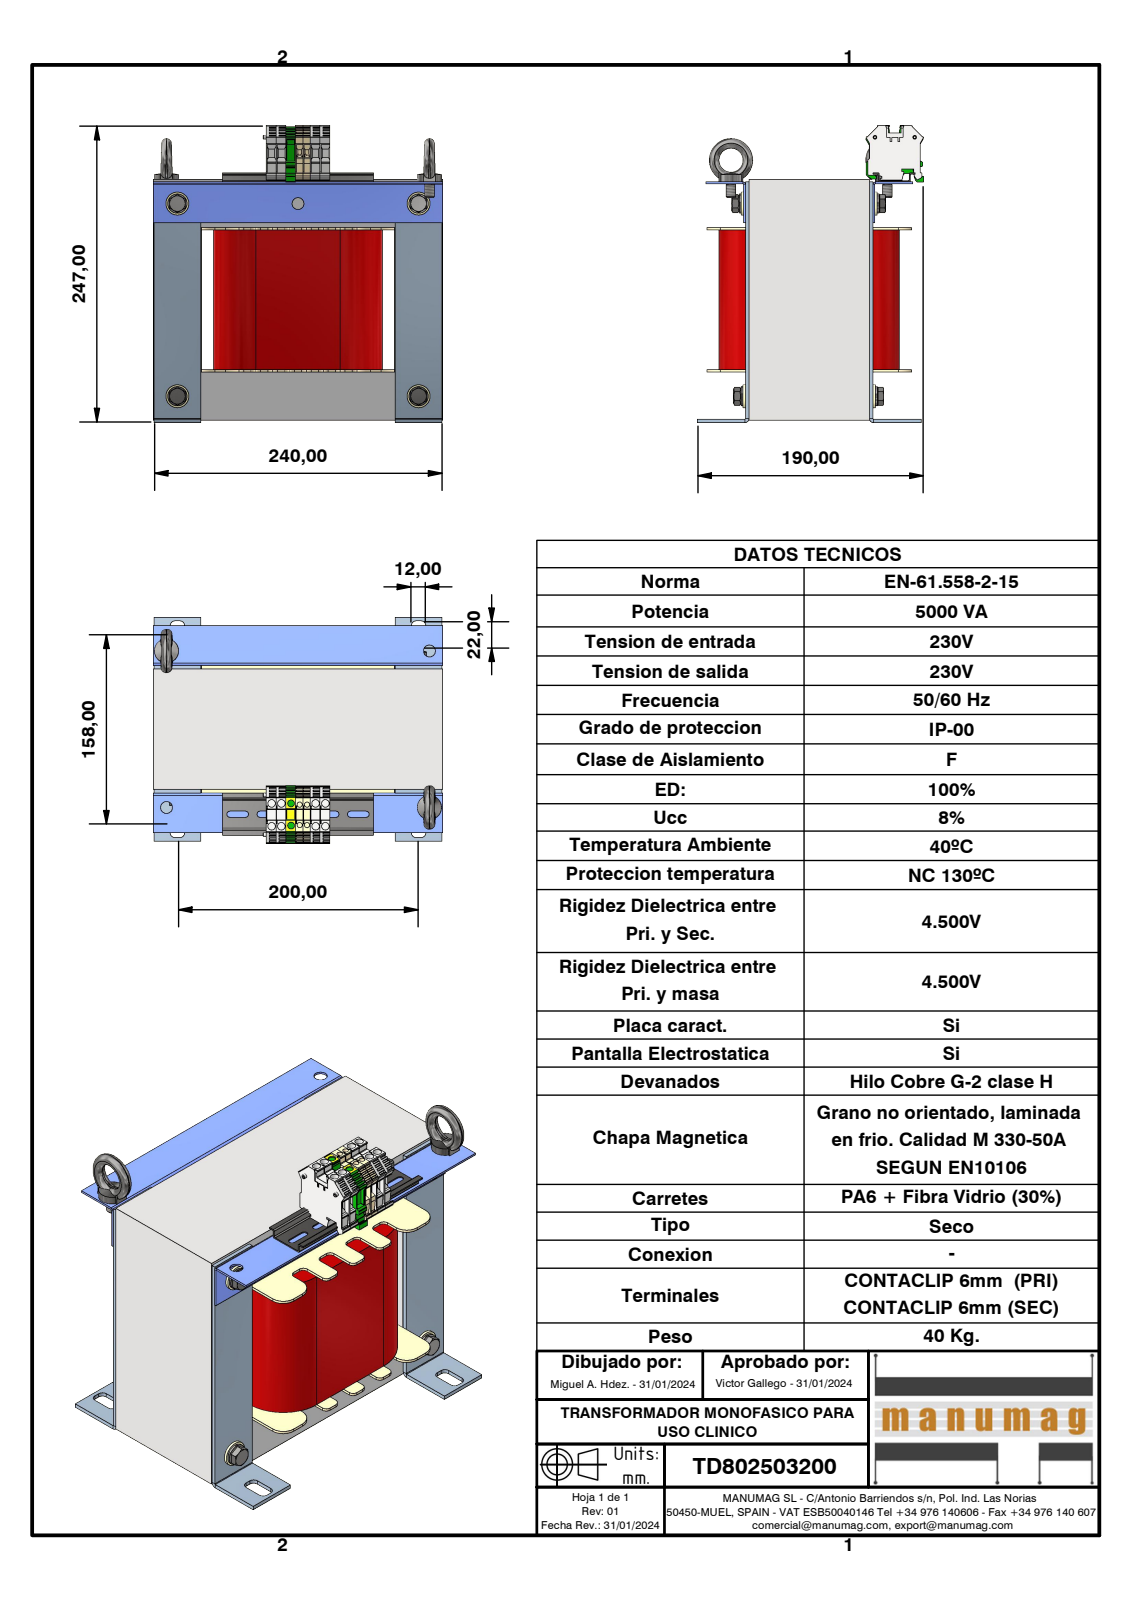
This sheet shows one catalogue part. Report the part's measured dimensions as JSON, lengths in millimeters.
{"part_name": "TD802503200; EI240 240 x 200 - 100 (Rc80); SEMI 40 X 60 RC80 EI240 - 50; Escuadra RC80 (+8 more)", "step_written_by": "Autodesk Inventor 2023 (AUTOMOTIVE_DESIGN)", "units": "millimeters", "bodies": {"solids": 42, "faces": 2415, "planar": 1680, "cylindrical": 567, "other": 168}, "overall_size": [247.05, 240, 188.1], "volume_mm3": 5536000, "surface_area_mm2": 623765, "round_holes": [[6.3, 8], [10, 7], [2.4, 4], [2.5, 4], [2.75, 4], [4.3, 4], [6.65, 4], [8, 4], [8.4, 4], [11, 4], [12, 4], [2.95, 2]], "round_bosses_or_shafts": [[19, 4], [16, 4], [11.4, 4], [9.6, 4], [7.32, 4], [36, 2], [8, 2], [7, 2]], "partial_cylinders_radius": [[4, 48], [0.3, 30], [1, 22], [0.25, 17], [0.5, 13], [2.6, 10], [2, 9], [0.4, 8]], "face_to_face_distances": [160, 40, 80, 100, 200, 3, 120, 103, 2, 1.5], "hole_center_spacings": [8.1, 15.23, 19, 20.65, 21.32, 23.56, 27.89, 36.5]}
